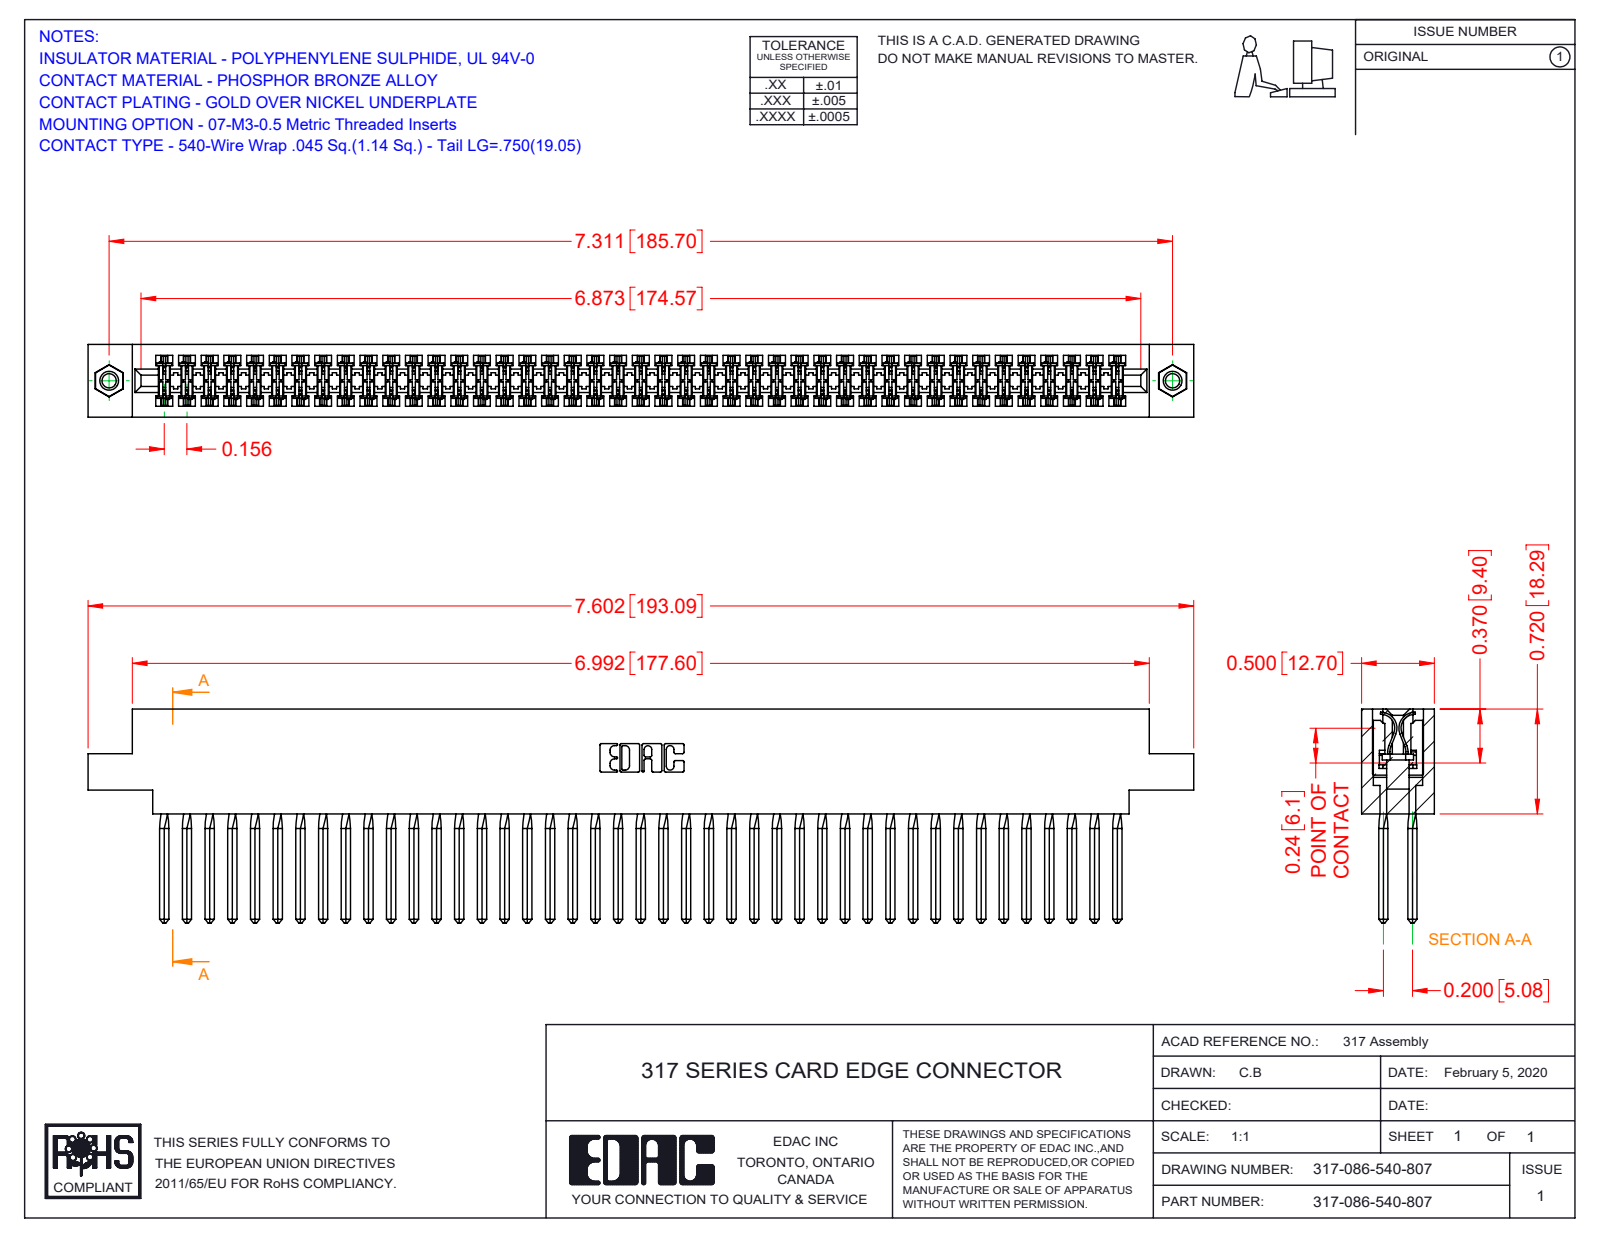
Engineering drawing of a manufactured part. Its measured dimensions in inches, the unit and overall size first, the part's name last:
Units: inches
Overall size (bounding box): 7.602 × 1.47 × 0.5
Round holes (diameter × count): ⌀0.098 ×2, ⌀0.125 ×2, ⌀0.156 ×2
Round bosses / shafts (diameter × count): ⌀0.155 ×2
Partial cylindrical surfaces — rounded edges, fillets, slot ends (radius × count): R0.015 ×172, R0.01 ×22, R0.007 ×6, R0.031 ×6, R0.026 ×3, R0.095 ×2, R0.1 ×2, R0.11 ×2
Main face-to-face distances: 0.5, 0.075, 0.425, 0.35, 0.195, 0.094, 0.2, 0.115, 0.131, 0.046
Hole centre spacings: 7.311
Volume: 1.979 in³ · Surface area: 75.05 in²
Bodies: 89 solids, 7816 faces (6368 planar, 1088 cylindrical, 360 other)
Part name (STEP PRODUCT): 317 Part_.156 Dia - TI; 317-086-540-807; 317-290-001_540; 345-250-001_345-250-005-103
STEP written by: SolidWorks 2016 (CONFIG_CONTROL_DESIGN)
